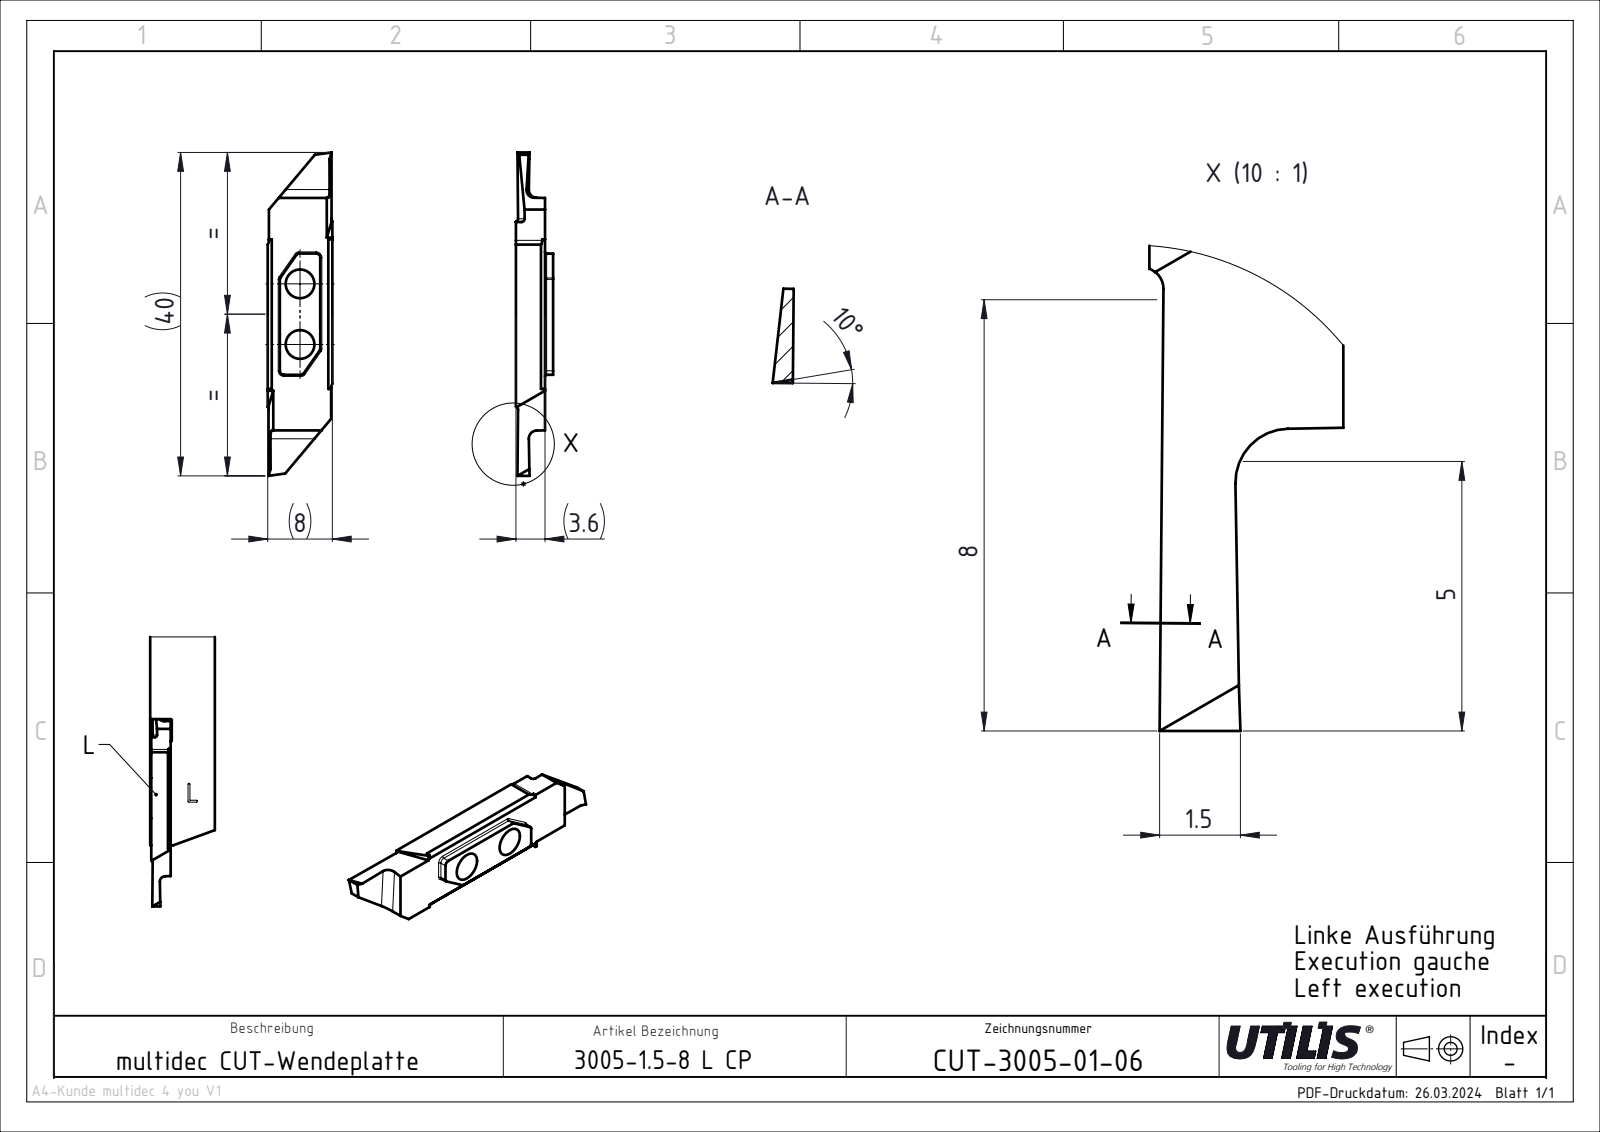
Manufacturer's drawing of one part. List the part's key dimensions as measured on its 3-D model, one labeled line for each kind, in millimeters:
Part name (STEP PRODUCT): CUT-3005 CP; ASME Y14.5
STEP written by: SolidWorks 2023 SP4 || FormatWorks Professional (AP242_MANAGED_MODEL_BASED_3D_ENGINEERING_MIM_LF)
Units: millimetres
Bodies: 1 solid, 32 faces (22 planar, 10 cylindrical, 0 other)
Overall size (bounding box): 40 × 8 × 3.6
Volume: 800 mm³ · Surface area: 853 mm²
Round holes (diameter × count): ⌀3.55 ×2
Partial cylindrical surfaces — rounded edges, fillets, slot ends (radius × count): R1 ×4, R0.4 ×2
Main face-to-face distances: 3.6, 8, 7.85, 22.54, 7.7, 40, 10.75, 29.25, 18.5
Hole centre spacings: 7.49
